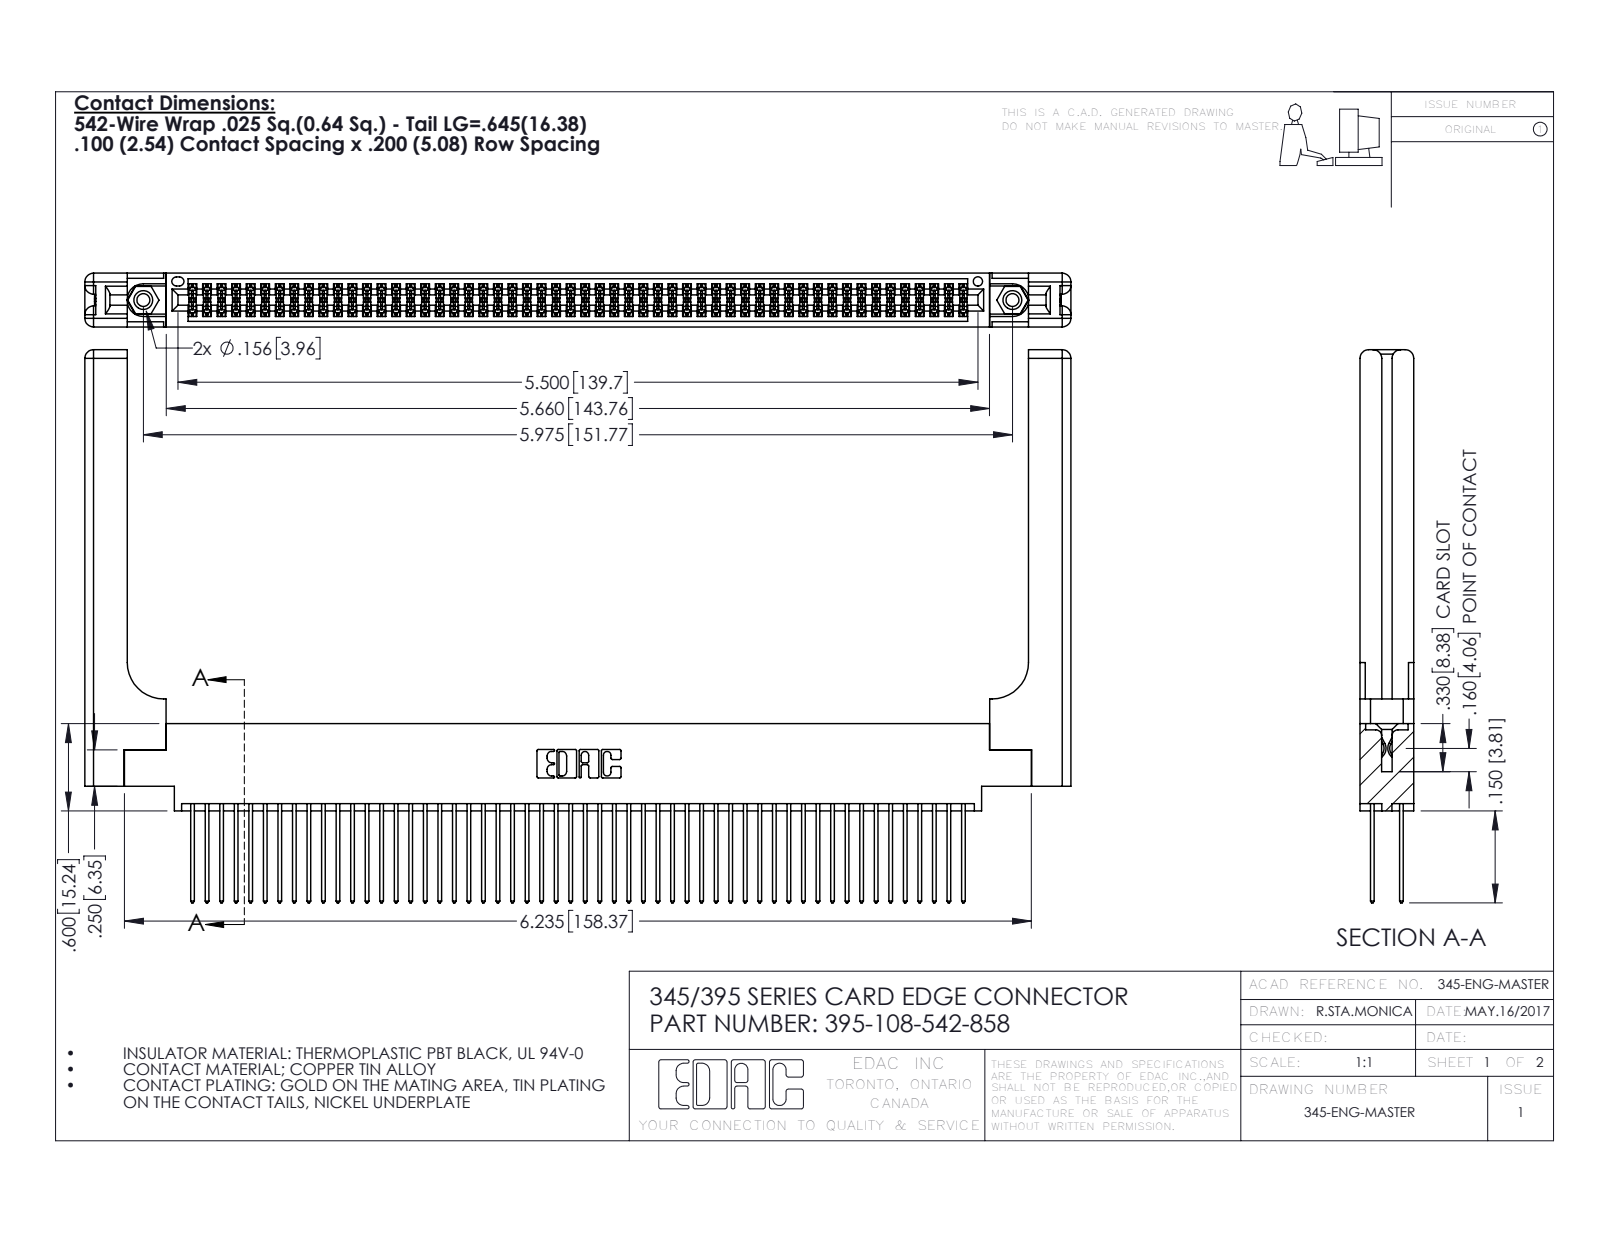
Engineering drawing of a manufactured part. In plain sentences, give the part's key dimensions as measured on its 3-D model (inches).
The part is named "345-250-001_345-250-001-102; 345 Part_0.170 Offset - 0.156 Dia-TH; 395-108-542-858; 345-292-001_345-293-142 (+1 more)". Its 3-D file was written by "SolidWorks 2016 (CONFIG_CONTROL_DESIGN)". It is 113 solids with 5786 faces: 3796 planar, 1930 cylindrical and 60 other. Overall it measures 6.779 by 3.802 by 0.37 inches. Its volume is 1.568 cubic inches and its surface area 51.54 square inches. Round holes: 2 of diameter 0.089, 2 of diameter 0.125, 2 of diameter 0.156, 1 of diameter 0.064. Round bosses or shafts: 2 of diameter 0.155. Partial cylindrical surfaces (rounded edges, fillets, slot ends): 162 of radius 0.006, 108 of radius 0.01, 22 of radius 0.01, 16 of radius 0.06, 6 of radius 0.007, 6 of radius 0.031, 3 of radius 0.026, 2 of radius 0.014. The main face-to-face distances are 0.072, 0.298, 0.37, 0.098, 0.272, 0.025, 0.2, 0.225, 0.175, 0.148. The hole center spacings are 0.27, 5.739, 5.975.
